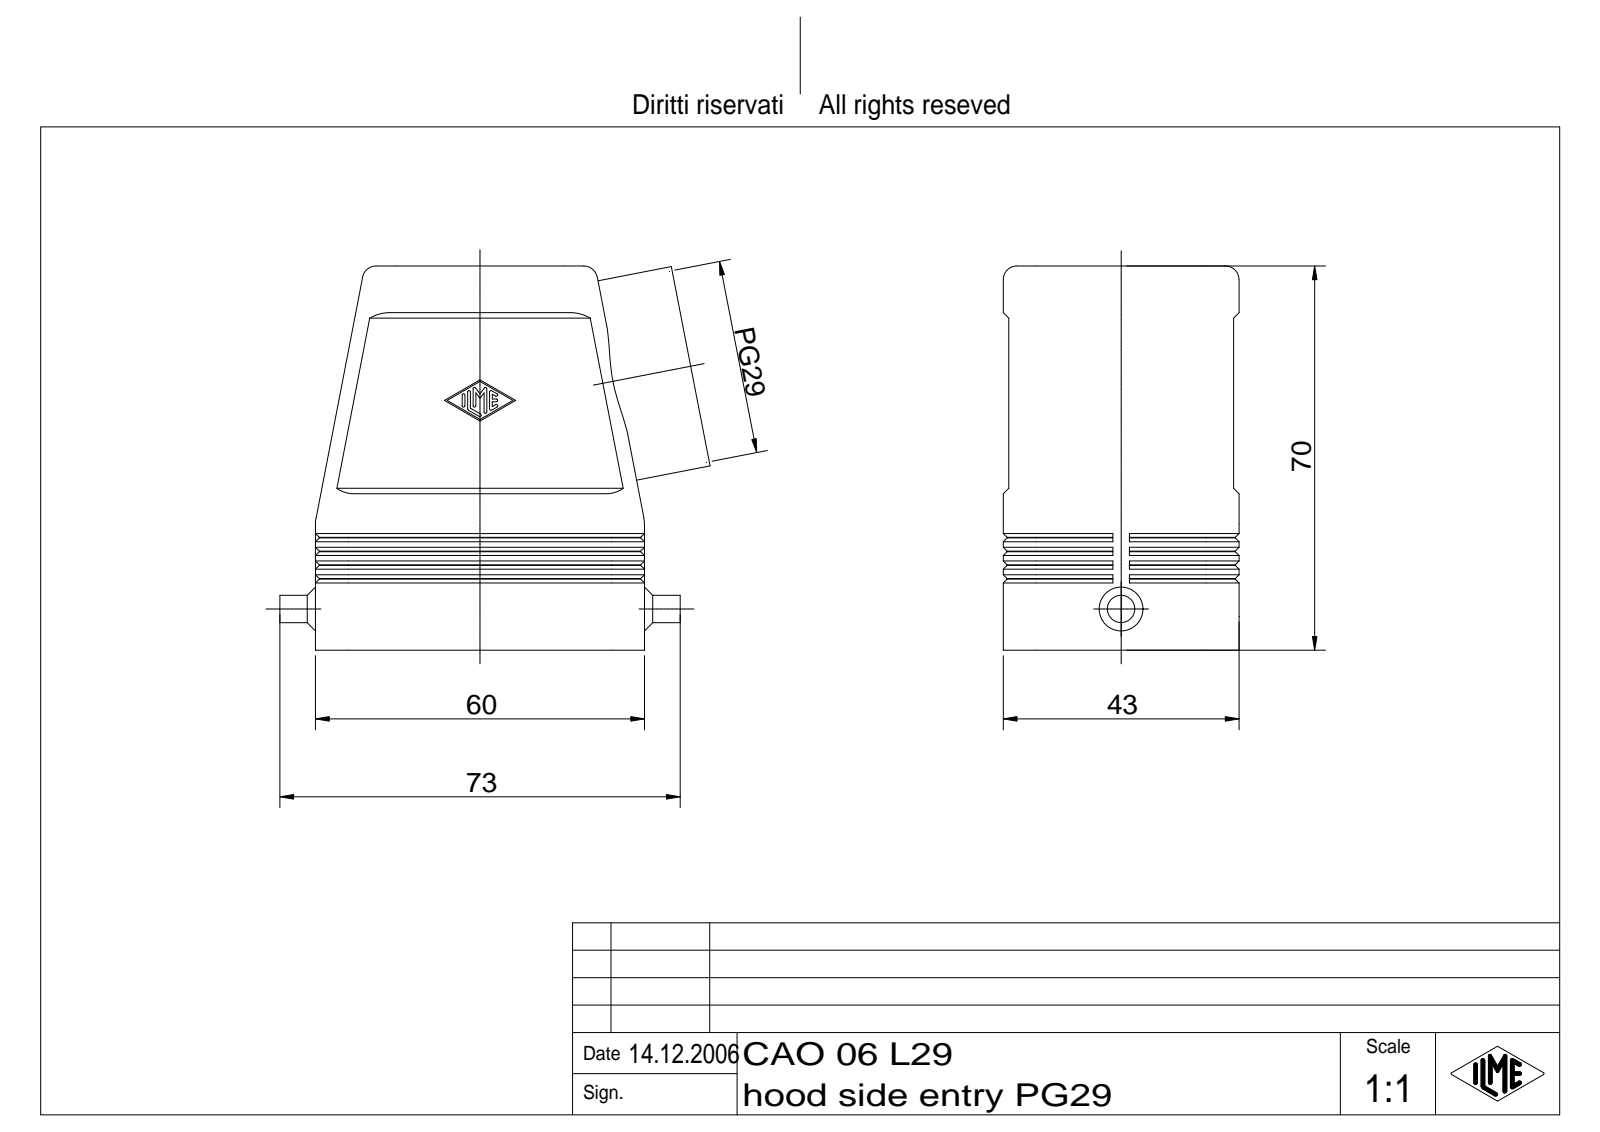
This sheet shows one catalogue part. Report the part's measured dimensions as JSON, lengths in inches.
{"part_name": "CAV Tüllengehäuse 1 Bügel für einen Einsatz", "step_written_by": "Autodesk Inventor 7 (AUTOMOTIVE_DESIGN)", "units": "inches", "bodies": {"solids": 1, "faces": 405, "planar": 156, "cylindrical": 108, "other": 141}, "overall_size": [3.089, 2.756, 1.693], "volume_in3": 3.251, "surface_area_in2": 47.08, "round_holes": [[1.318, 1], [1.397, 1]], "round_bosses_or_shafts": [[1.457, 1], [0.197, 1]], "partial_cylinders_radius": [[0.01, 14], [0.236, 10], [0.079, 4], [0.098, 4], [0.118, 4], [0.209, 2]], "face_to_face_distances": [0.157, 1.496, 0.118, 1.378, 0.039, 1.535, 1.654, 1.614, 0.197, 0.276]}
